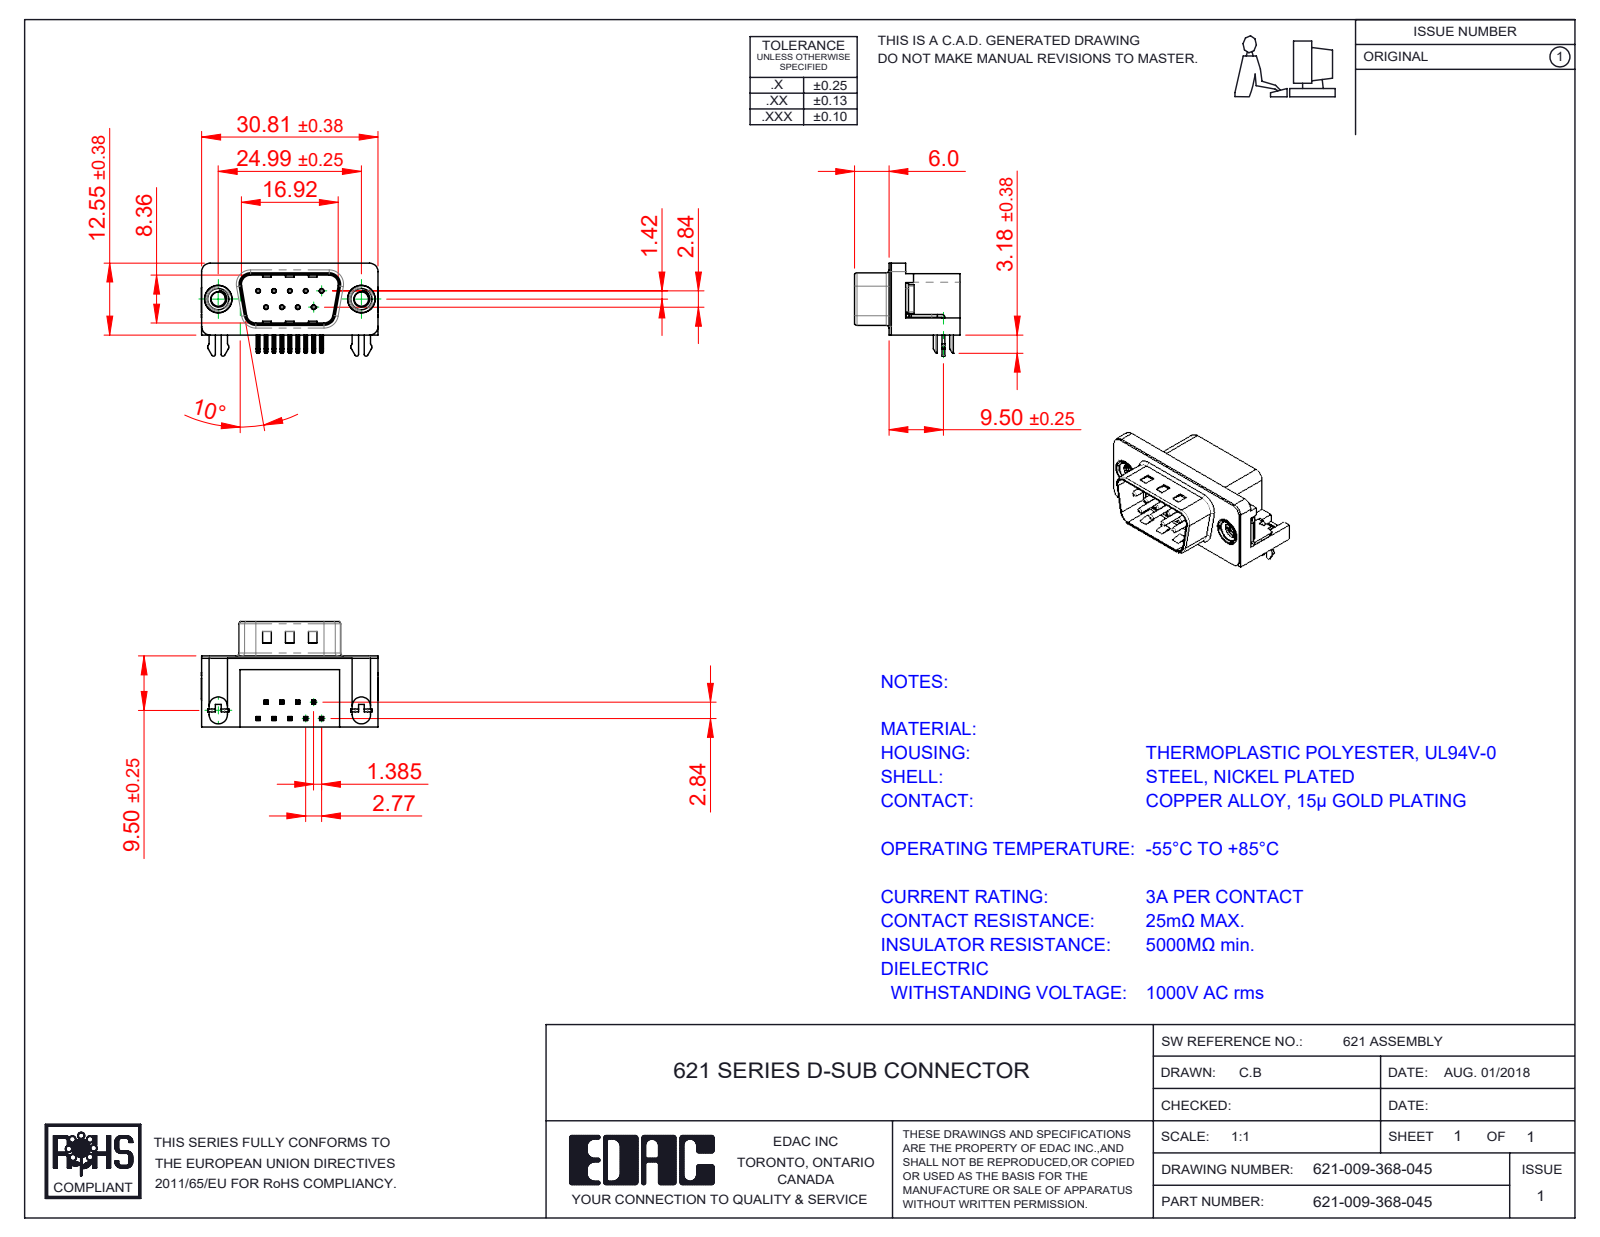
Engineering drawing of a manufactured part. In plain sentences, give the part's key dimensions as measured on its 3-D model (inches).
The part is named "621 M3 Threaded Rivet; 621 Contact Bottom; 621-009-368-045; 621 Shell_9 Socket (+3 more)". Its 3-D file was written by "SolidWorks 2016 (CONFIG_CONTROL_DESIGN)". It is 15 solids with 1111 faces: 615 planar, 325 cylindrical and 171 other. Overall it measures 1.216 by 0.724 by 0.64 inches. Its volume is 0.198 cubic inches and its surface area 6.973 square inches. Round holes: 9 of diameter 0.014, 9 of diameter 0.031, 2 of diameter 0.079, 2 of diameter 0.098, 2 of diameter 0.157, 2 of diameter 0.189, 2 of diameter 0.197. Round bosses or shafts: 9 of diameter 0.03, 2 of diameter 0.193, 2 of diameter 0.187, 2 of diameter 0.154, 2 of diameter 0.118. Partial cylindrical surfaces (rounded edges, fillets, slot ends): 48 of radius 0.01, 18 of radius 0.005, 16 of radius 0.039, 9 of radius 0.02, 8 of radius 0.059, 8 of radius 0.063, 4 of radius 0.035, 4 of radius 0.079. The main face-to-face distances are 0.016, 0.472, 0.488, 0.407, 0.114, 0.374, 0.098, 0.083, 0.014, 0.421. The hole center spacings are 0.124, 0.109, 0.218, 0.198, 0.198, 0.327, 0.294, 0.295.
